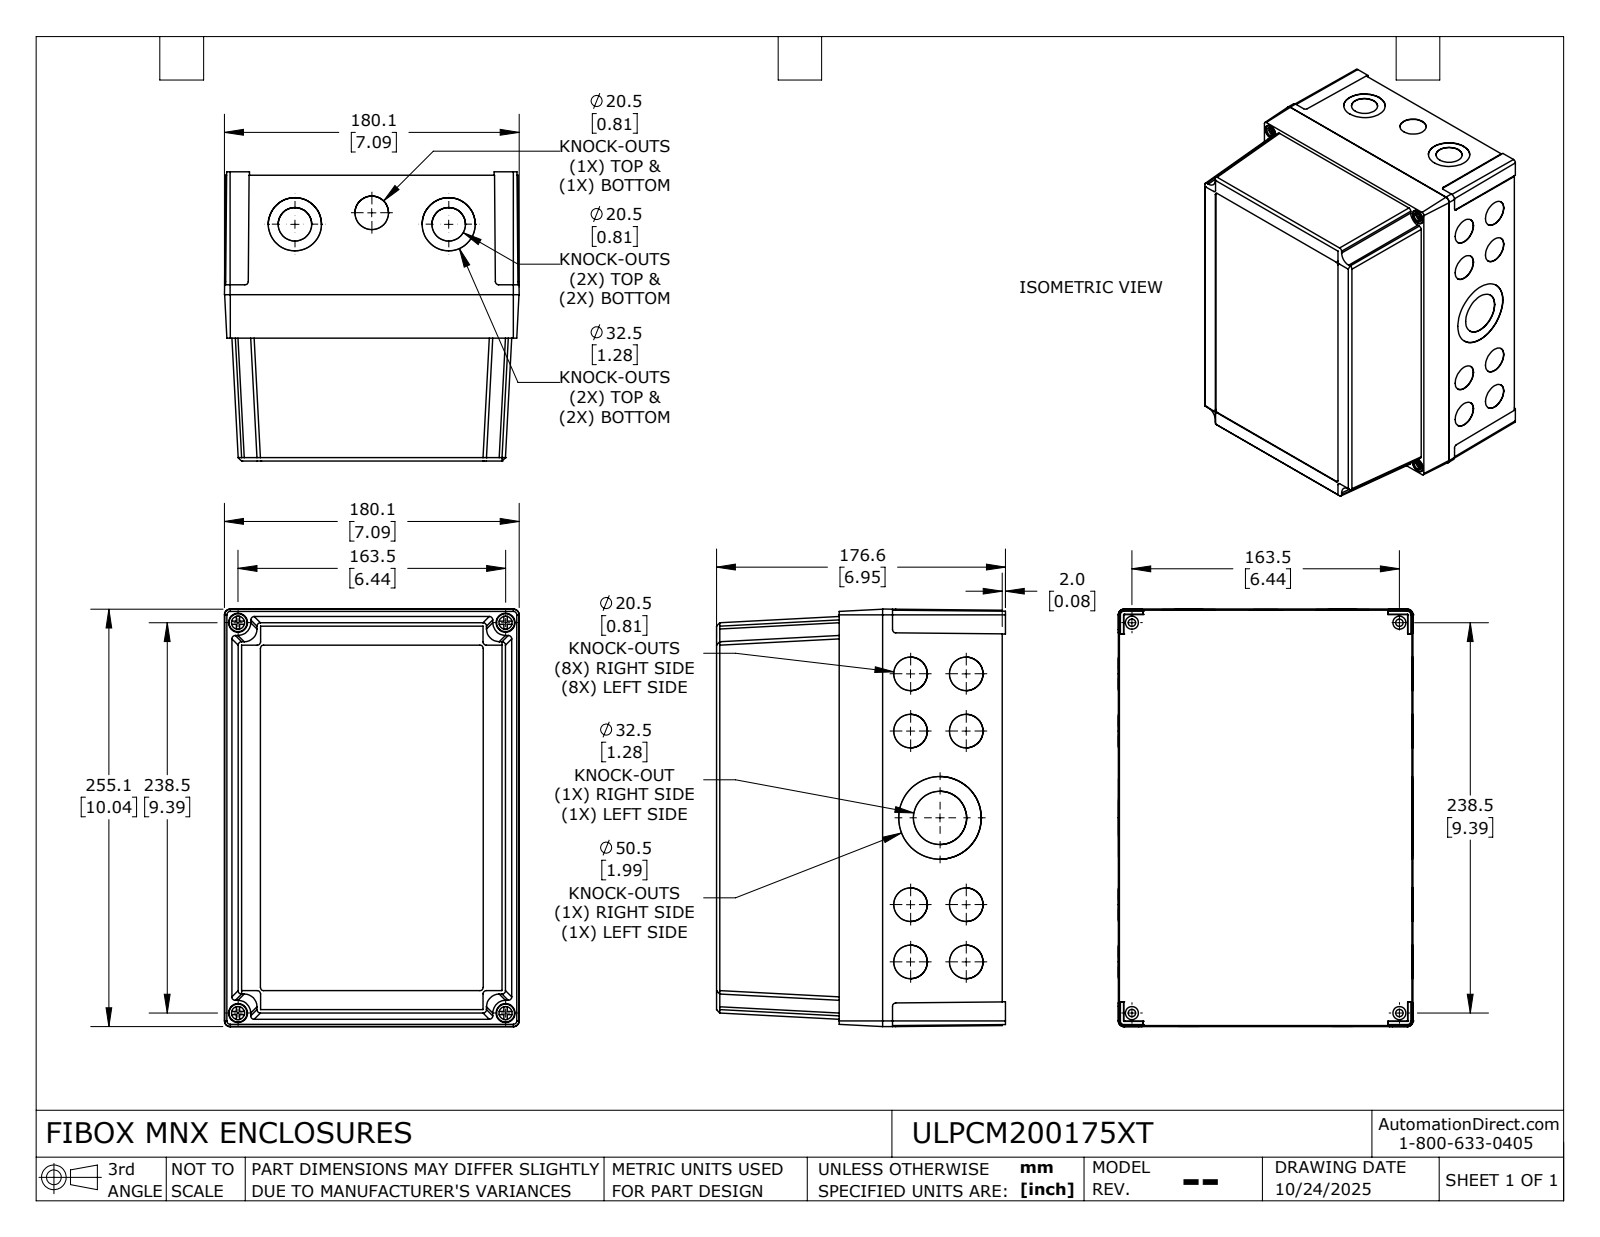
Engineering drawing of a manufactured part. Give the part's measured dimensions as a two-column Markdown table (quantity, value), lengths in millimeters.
| quantity | value |
| --- | --- |
| part name | ULPCM200175XT_Default |
| STEP written by | SolidWorks 2024 (CONFIG_CONTROL_DESIGN) |
| units | millimeters |
| bodies | 6 solids, 791 faces (437 planar, 308 cylindrical, 46 other) |
| overall size | 255.1 × 180.1 × 176.6 |
| volume | 681 500 mm³ |
| surface area | 481 000 mm² |
| round holes (diameter × count) | 20.5 × 22, 3.2 × 20, 4 × 20, 32.5 × 6, 4.5 × 4, 8 × 4, 11.6 × 4, 50.5 × 2 |
| round bosses / shafts (diameter × count) | 8 × 16, 2.5 × 8, 11 × 4, 7.2 × 4, 7 × 4 |
| partial cylindrical surfaces (radius × count) | 2 × 8, 2.1 × 8, 2.8 × 6, 1.1 × 4, 5 × 4, 7.8 × 4, 1.2 × 2 |
| main face-to-face distances | 1.5, 3, 171.6, 4.2, 168.6, 2.5, 174.1, 171.1, 4.6, 3 |
| hole center spacings | 35, 34, 48.8, 49.3, 128.2, 141, 145, 125 |
